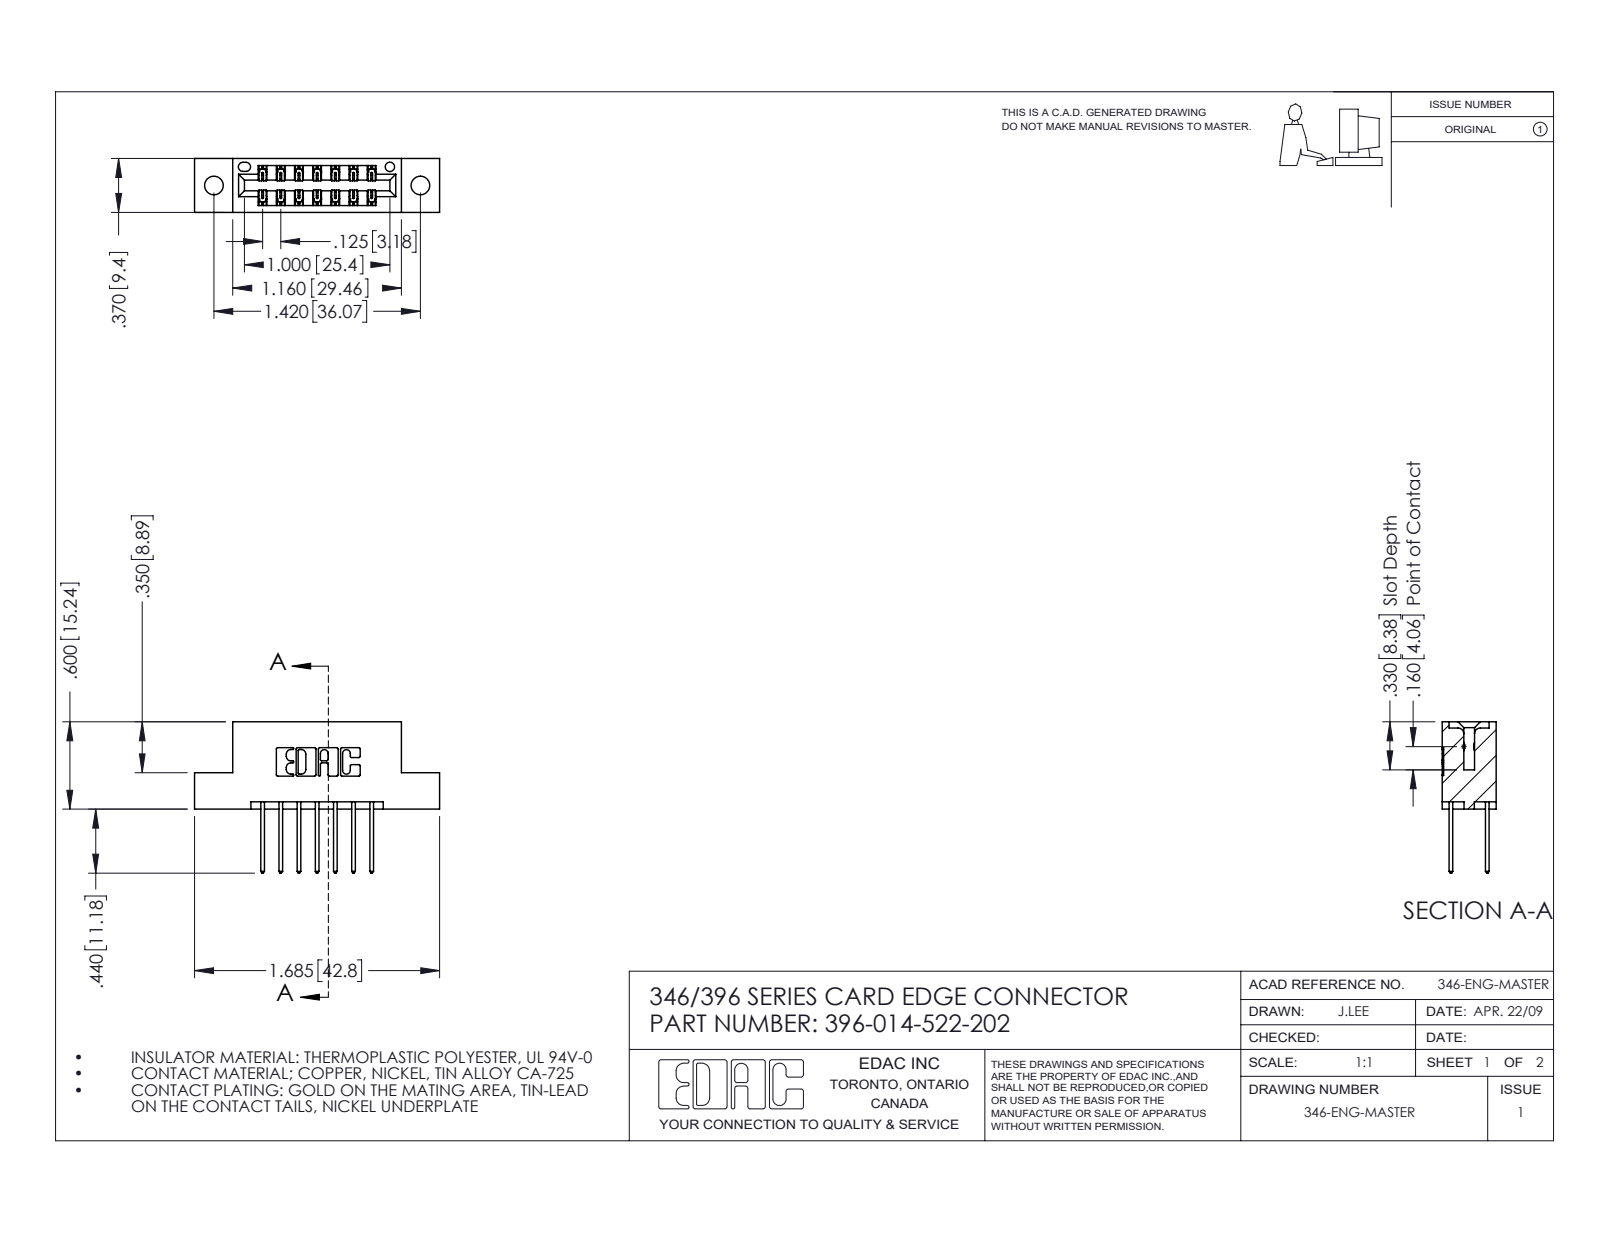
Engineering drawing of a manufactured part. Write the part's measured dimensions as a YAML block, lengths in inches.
part_name: "396-014-522-202; 345-292-001_345-293-122; 346 Part_Flush Mounting Lugs - 0.128 Dia"
step_written_by: "SolidWorks 2016 (CONFIG_CONTROL_DESIGN)"
units: inches
bodies: {solids: 15, faces: 850, planar: 566, cylindrical: 284, other: 0}
overall_size: [1.685, 1.04, 0.37]
volume: 0.238
surface_area: 7.299
round_holes:
  - {diameter: 0.128, count: 2}
  - {diameter: 0.064, count: 1}
partial_cylinders:
  - {radius: 0.01, count: 22}
  - {radius: 0.006, count: 21}
  - {radius: 0.01, count: 14}
  - {radius: 0.007, count: 6}
  - {radius: 0.031, count: 6}
  - {radius: 0.026, count: 3}
  - {radius: 0.014, count: 2}
  - {radius: 0.022, count: 2}
face_to_face_distances: [0.25, 0.048, 0.322, 0.37, 0.025, 0.072, 0.298, 0.275, 0.148, 0.222]
hole_center_spacings: [0.246, 1.217, 1.42]
